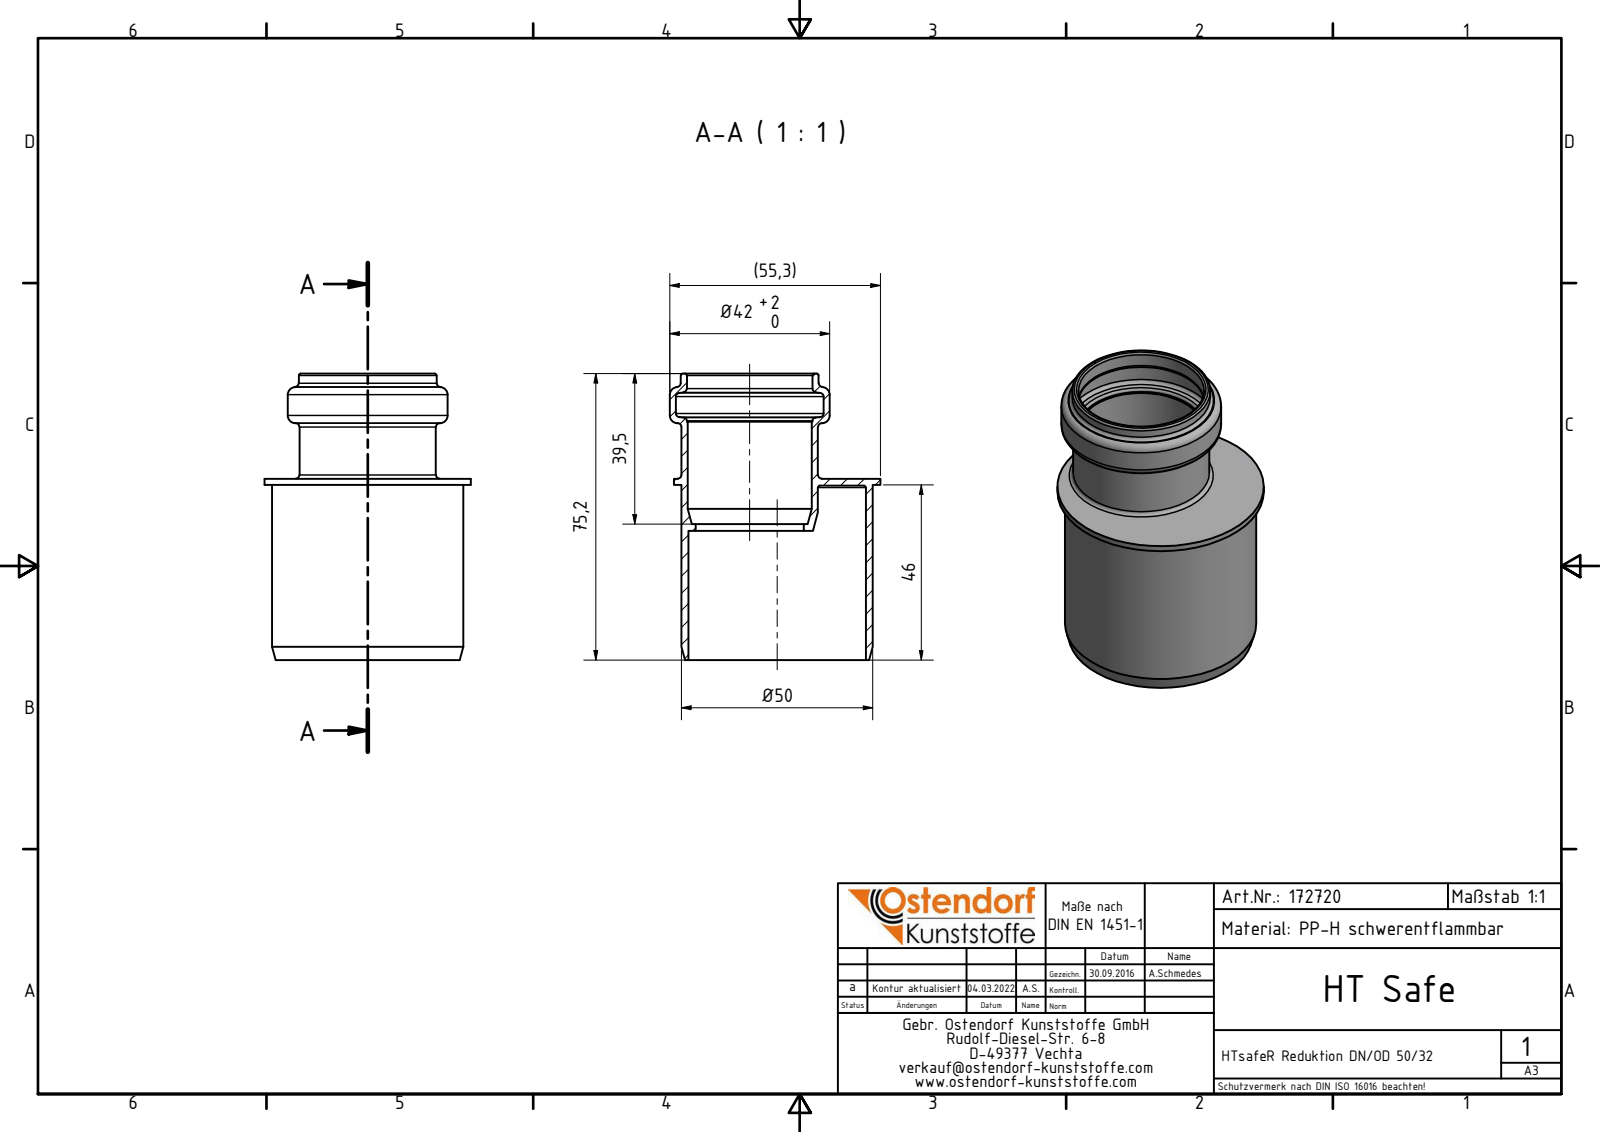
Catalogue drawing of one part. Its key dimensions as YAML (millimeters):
part_name: "172720 HTsafeR DN_OD 50_32"
step_written_by: "Autodesk Inventor 2020 (AUTOMOTIVE_DESIGN)"
units: millimeters
bodies: {solids: 1, faces: 40, planar: 8, cylindrical: 12, other: 20}
overall_size: [75.2, 55.3, 54.2]
volume: 22707
surface_area: 26293
round_holes:
  - {diameter: 28.4, count: 1}
  - {diameter: 32.6, count: 1}
  - {diameter: 33, count: 1}
  - {diameter: 38.8, count: 1}
  - {diameter: 46.6, count: 1}
round_bosses_or_shafts:
  - {diameter: 54.2, count: 1}
  - {diameter: 50.2, count: 1}
  - {diameter: 42, count: 1}
  - {diameter: 36.2, count: 1}
  - {diameter: 35.8, count: 1}
face_to_face_distances: [1.8, 1.6, 11.9, 12.1, 13.7, 33.9, 45.8, 46, 47.6, 35.7]
hole_center_spacings: [7.2]
